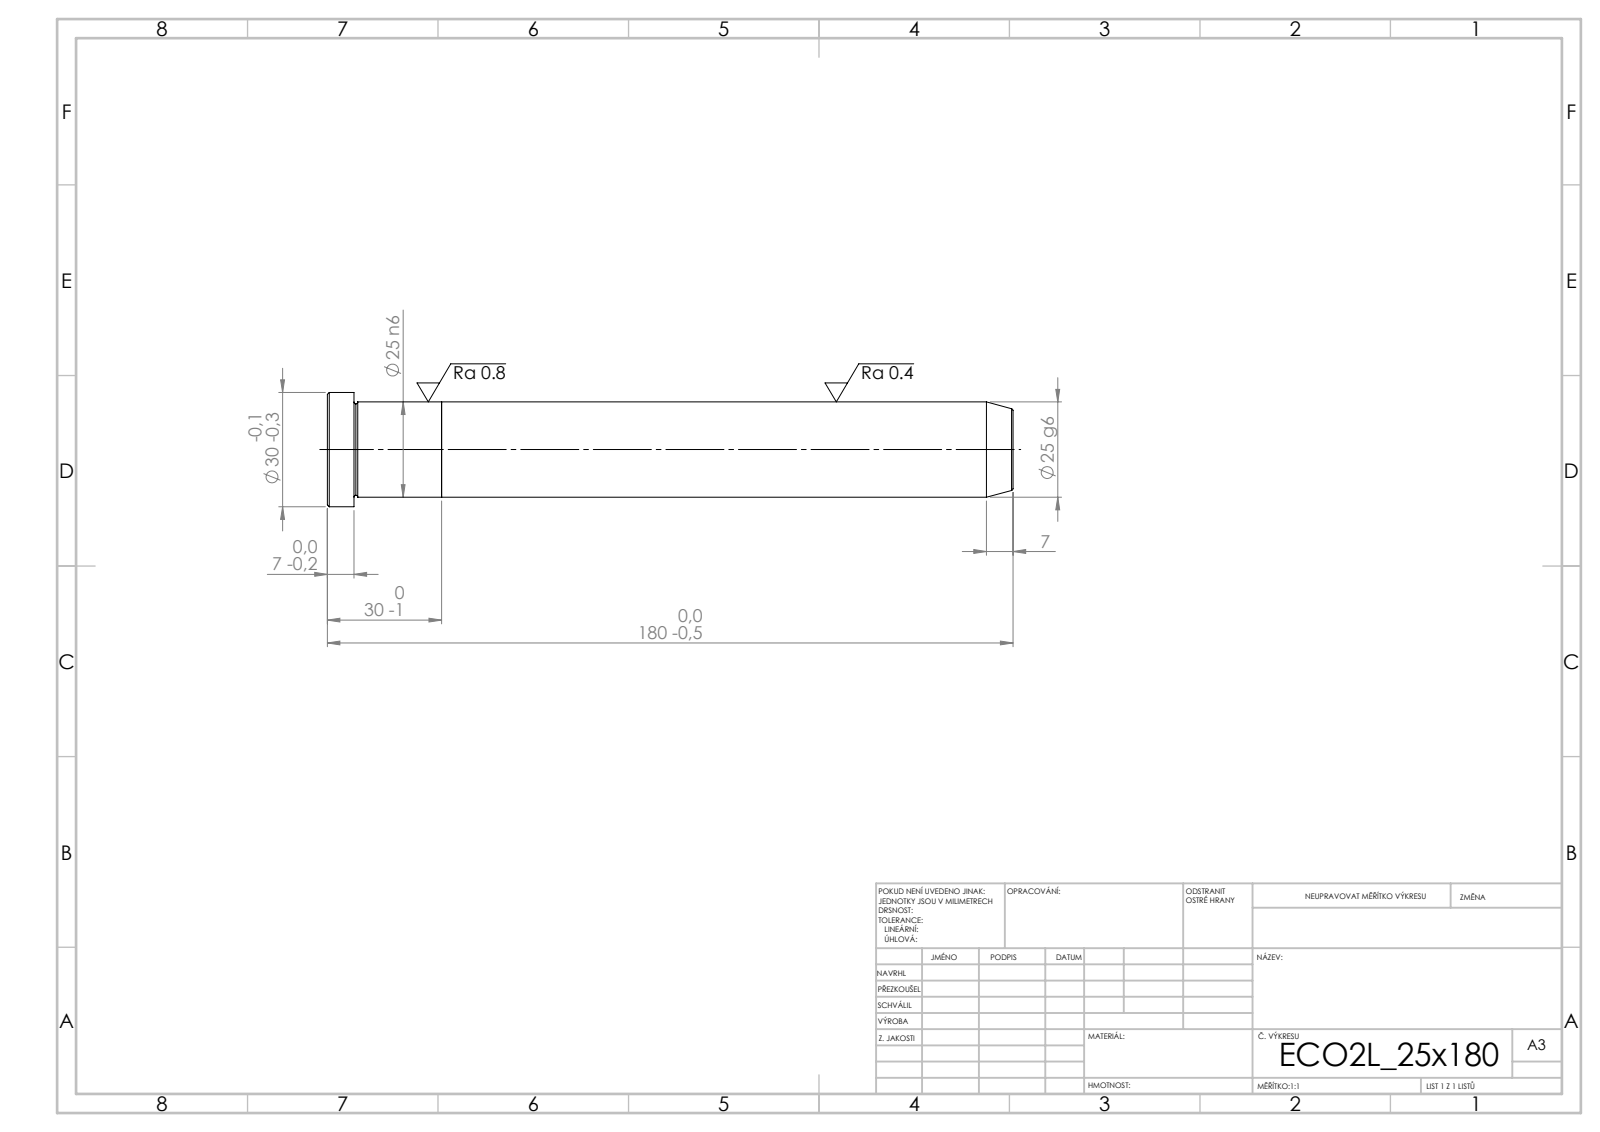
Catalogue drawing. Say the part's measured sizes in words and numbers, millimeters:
Its 3-D file was written by "SolidWorks 2019 (CONFIG_CONTROL_DESIGN)". It is 2 solids with 21 faces: 5 planar, 6 cylindrical and 10 other. Overall it measures 180 by 30 by 30 millimeters. Its volume is 89 336 cubic millimeters and its surface area 16 489 square millimeters. Round bosses or shafts: 1 of diameter 30, 1 of diameter 25. The main face-to-face distances are 30, 150, 180, 173, 23, 7.
